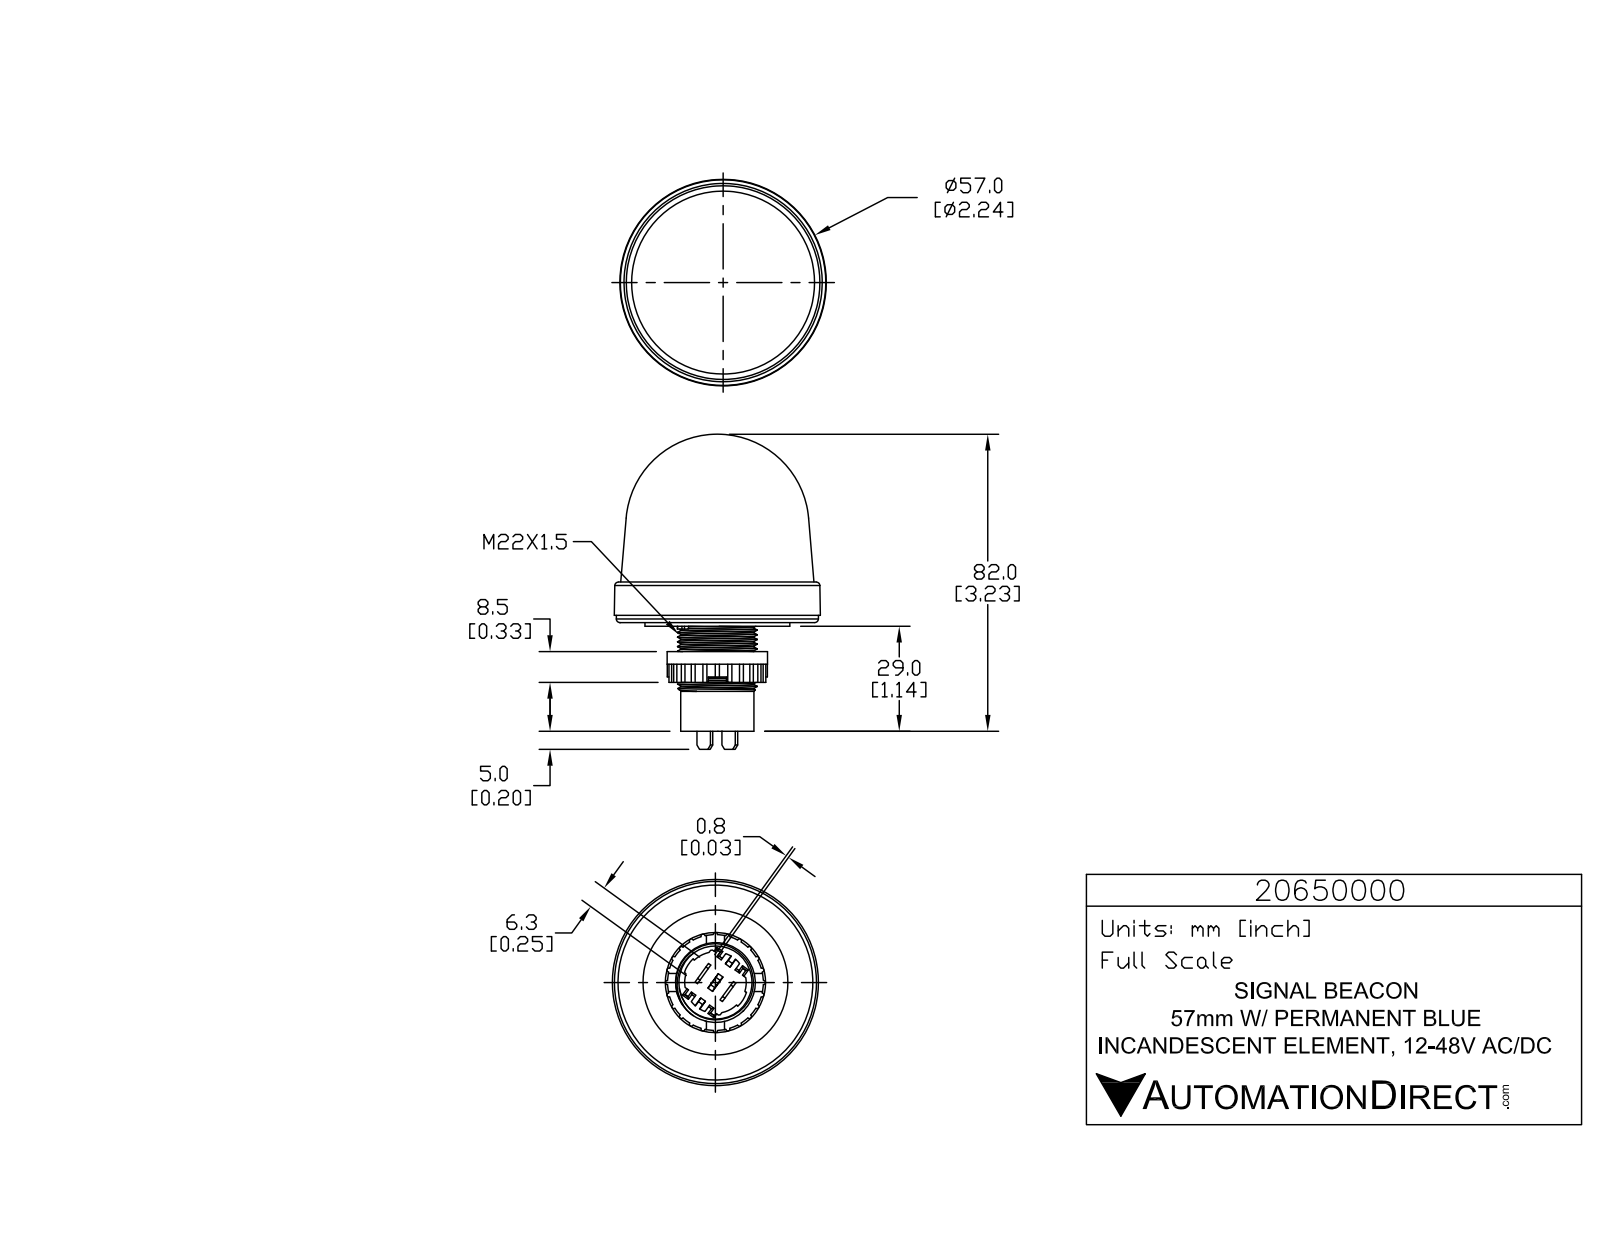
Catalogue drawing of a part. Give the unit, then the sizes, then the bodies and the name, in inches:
Units: inches
Overall size (bounding box): 3.413 × 2.24 × 2.24
Round holes (diameter × count): ⌀0.039 ×3, ⌀0.906 ×1
Round bosses / shafts (diameter × count): ⌀0.226 ×3, ⌀0.056 ×3, ⌀2.197 ×1, ⌀1.575 ×1, ⌀1.091 ×1, ⌀0.866 ×1, ⌀0.795 ×1
Partial cylindrical surfaces — rounded edges, fillets, slot ends (radius × count): R0.023 ×24, R0.008 ×6, R0.008 ×6, R0.008 ×6, R0.131 ×6, R0.004 ×3, R0.005 ×3, R0.008 ×3
Main face-to-face distances: 0.039, 0.276, 0.335, 0.315, 1.063, 0.748, 1.024, 0.118, 1.142, 0.413
Volume: 6.481 in³ · Surface area: 26.07 in²
Bodies: 1 solid, 1002 faces (637 planar, 266 cylindrical, 99 other)
Part name (STEP PRODUCT): 20650000
STEP written by: SolidWorks 2015 (AUTOMOTIVE_DESIGN)
